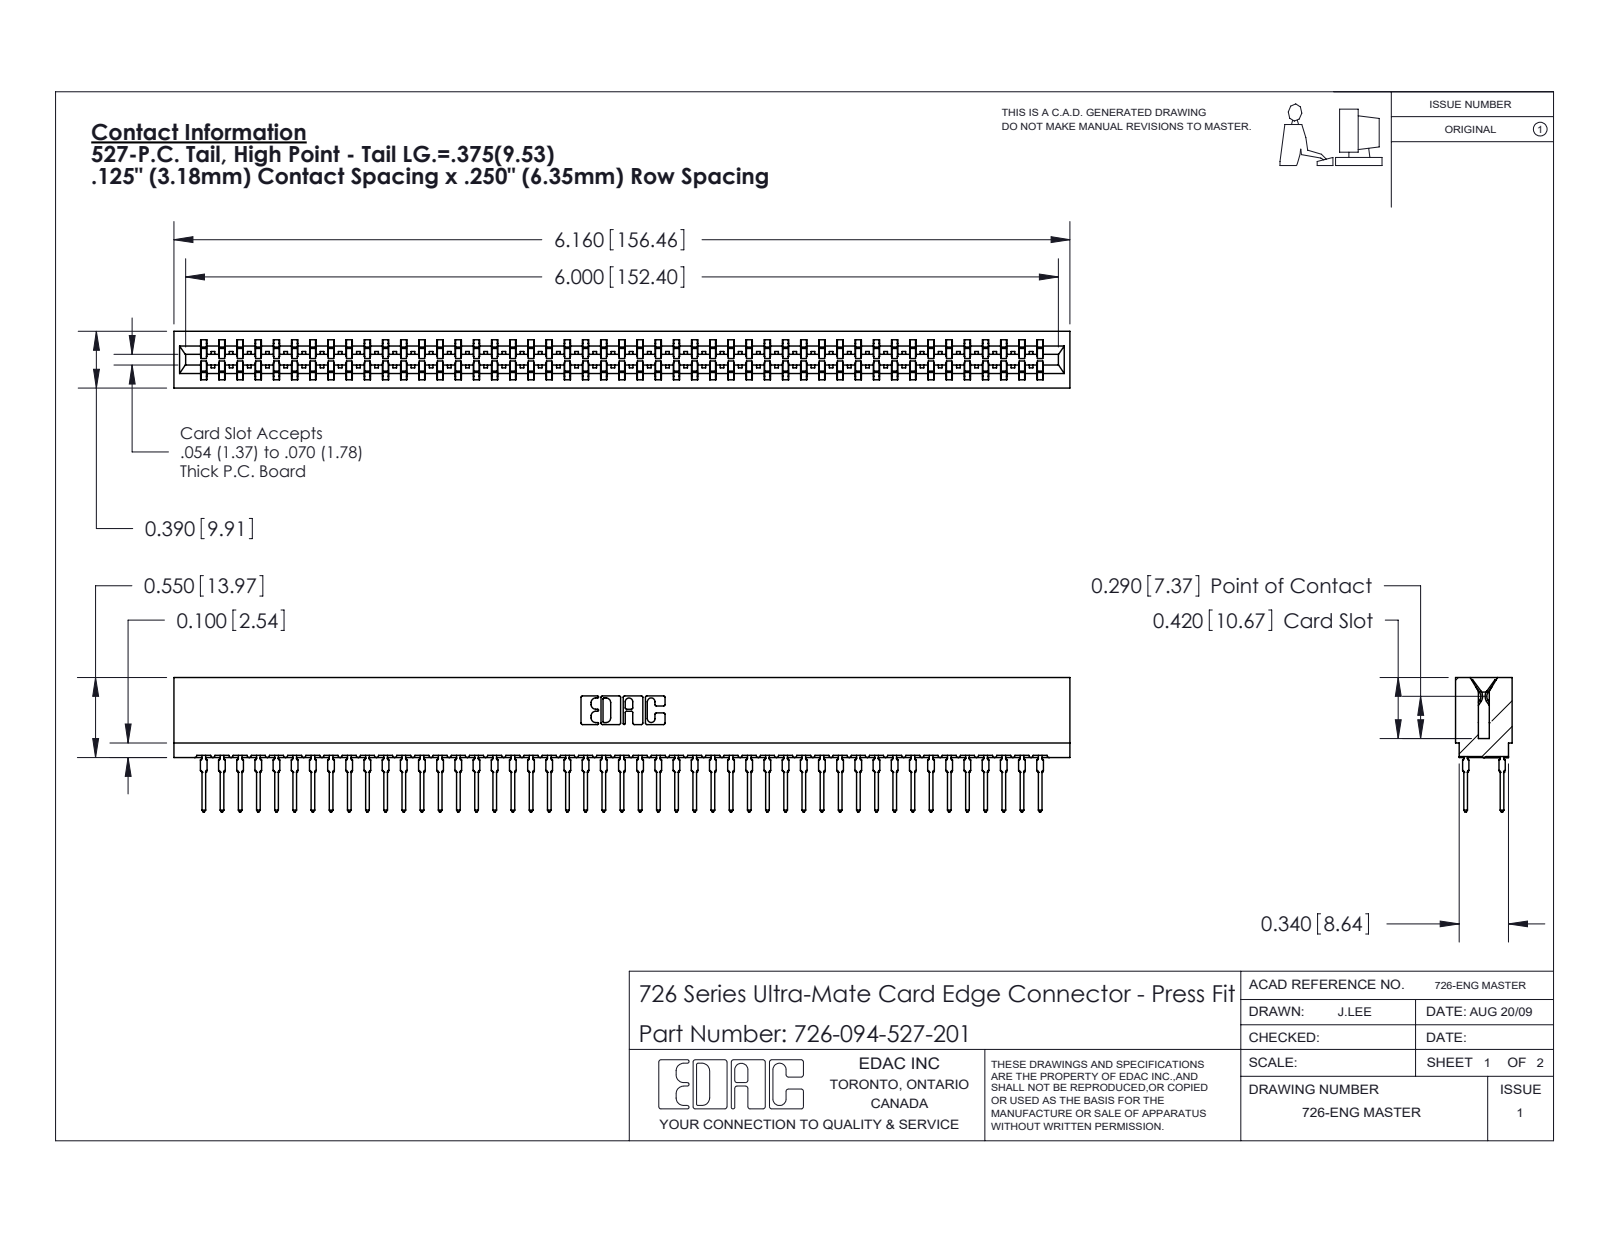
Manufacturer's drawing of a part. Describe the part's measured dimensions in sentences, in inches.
The part is named "746-292-001_527; 726 Part_.515 Slot Depth - 01; 726-094-527-201". Its 3-D file was written by "SolidWorks 2020 (CONFIG_CONTROL_DESIGN)". It is 95 solids with 8510 faces: 4379 planar, 1687 cylindrical and 2444 other. Overall it measures 6.16 by 0.924 by 0.39 inches. Its volume is 0.886 cubic inches and its surface area 38.81 square inches. Partial cylindrical surfaces (rounded edges, fillets, slot ends): 188 of radius 0.021, 48 of radius 0.015, 22 of radius 0.01, 8 of radius 0.005, 8 of radius 0.011, 6 of radius 0.007, 6 of radius 0.031, 3 of radius 0.026. The main face-to-face distances are 0.057, 0.333, 0.025, 0.307, 0.39, 0.25, 0.275, 0.083, 0.365, 0.032.
